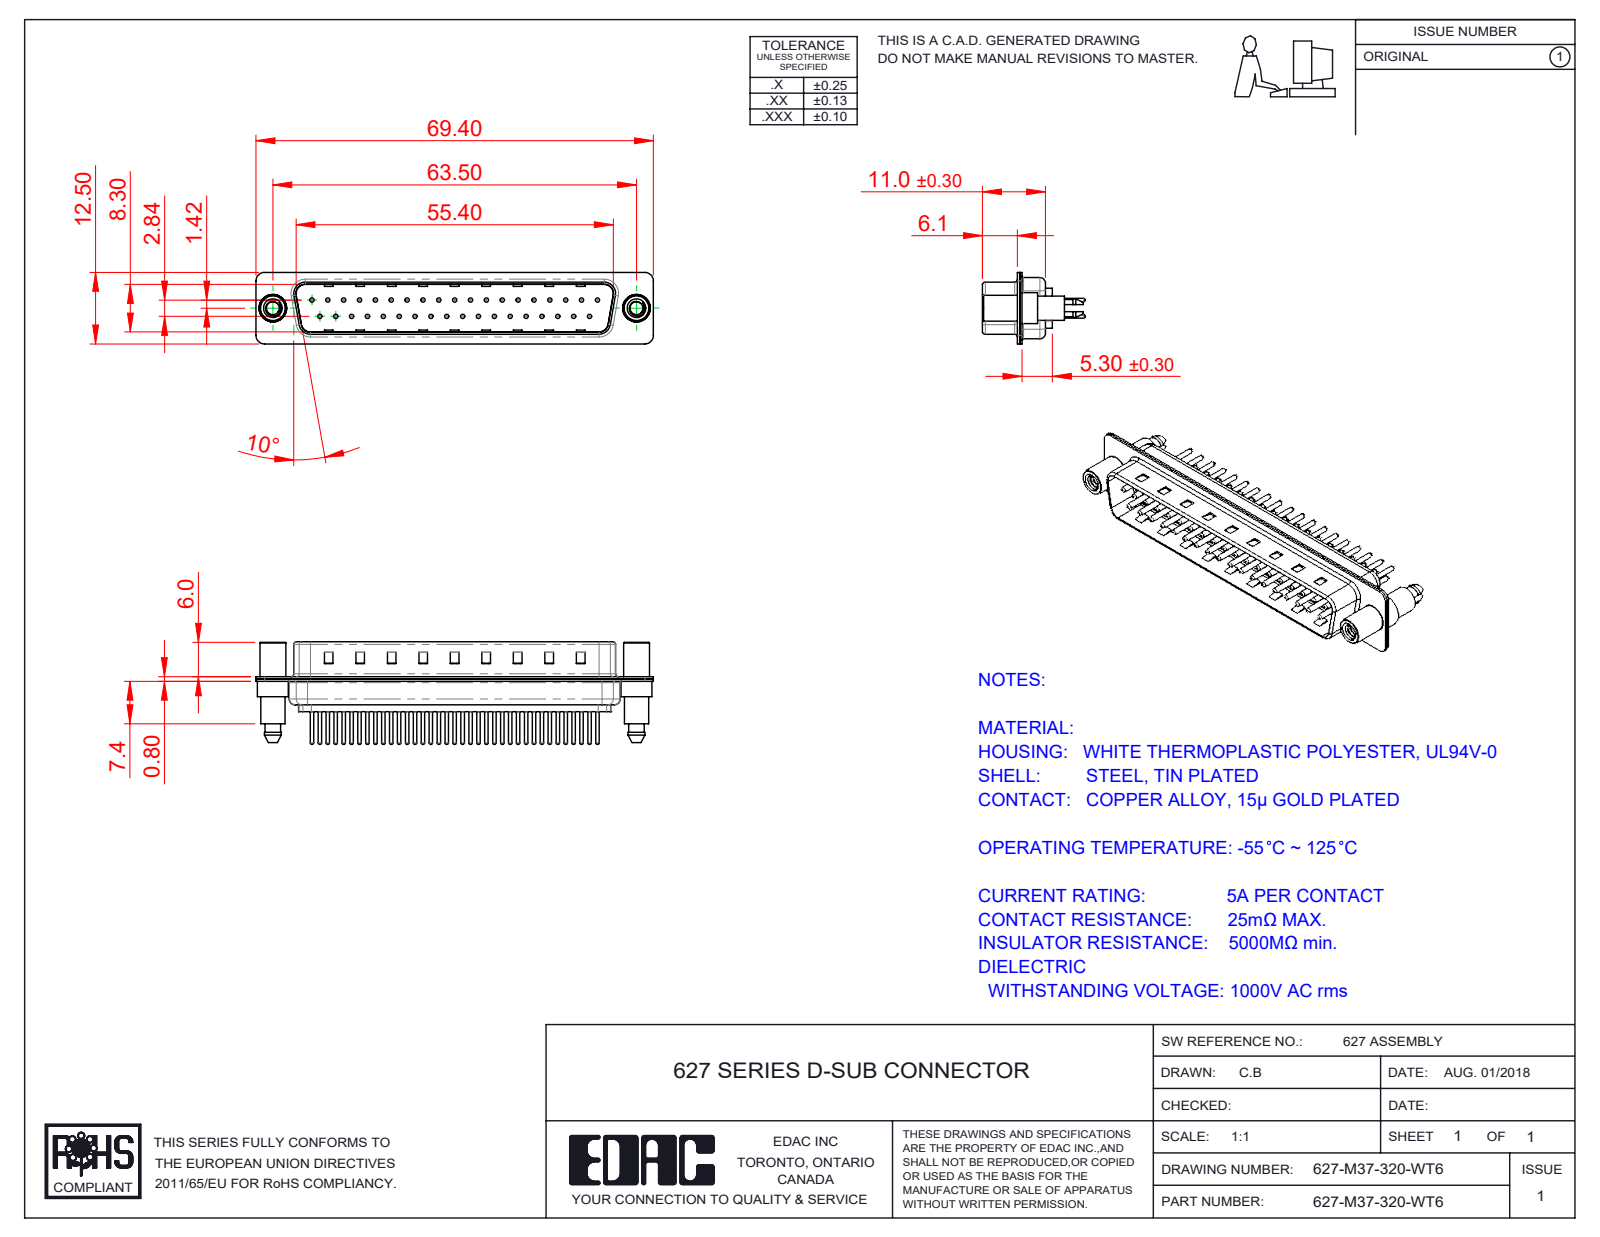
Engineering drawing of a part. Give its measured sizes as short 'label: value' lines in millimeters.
name: 627M 4-40 Threaded Standoff and Boardlock; 627M Contact Row 1_20; 627M Housing_37 Contacts; 627-M37-320-WT6 (+3 more)
written by: SolidWorks 2020 (CONFIG_CONTROL_DESIGN)
unit: mm
bodies: 42 solids, 1833 faces (480 planar, 687 cylindrical, 666 other)
size: 69.4 × 17.9 × 12.5
volume: 4 106 mm³; area: 9 737 mm²
holes: 37× ⌀0.75, 37× ⌀1.6, 37× ⌀2, 2× ⌀2.26, 2× ⌀4, 2× ⌀4.8
bosses: 37× ⌀1.5, 37× ⌀0.6, 2× ⌀5.4, 2× ⌀4.9, 2× ⌀4.5, 2× ⌀4.25
rounds: 18× R1.5, 12× R2, 10× R1.6, 8× R0.5, 4× R0.25, 4× R0.6, 4× R0.65, 4× R0.9
face distances: 0.4, 0.8, 9.5, 9.1, 8.7, 9.9, 1.2, 5.7, 0.75, 0.35
hole spacings: 2.77, 5.54, 3.16, 8.31, 11.08, 13.85, 16.62, 19.39
